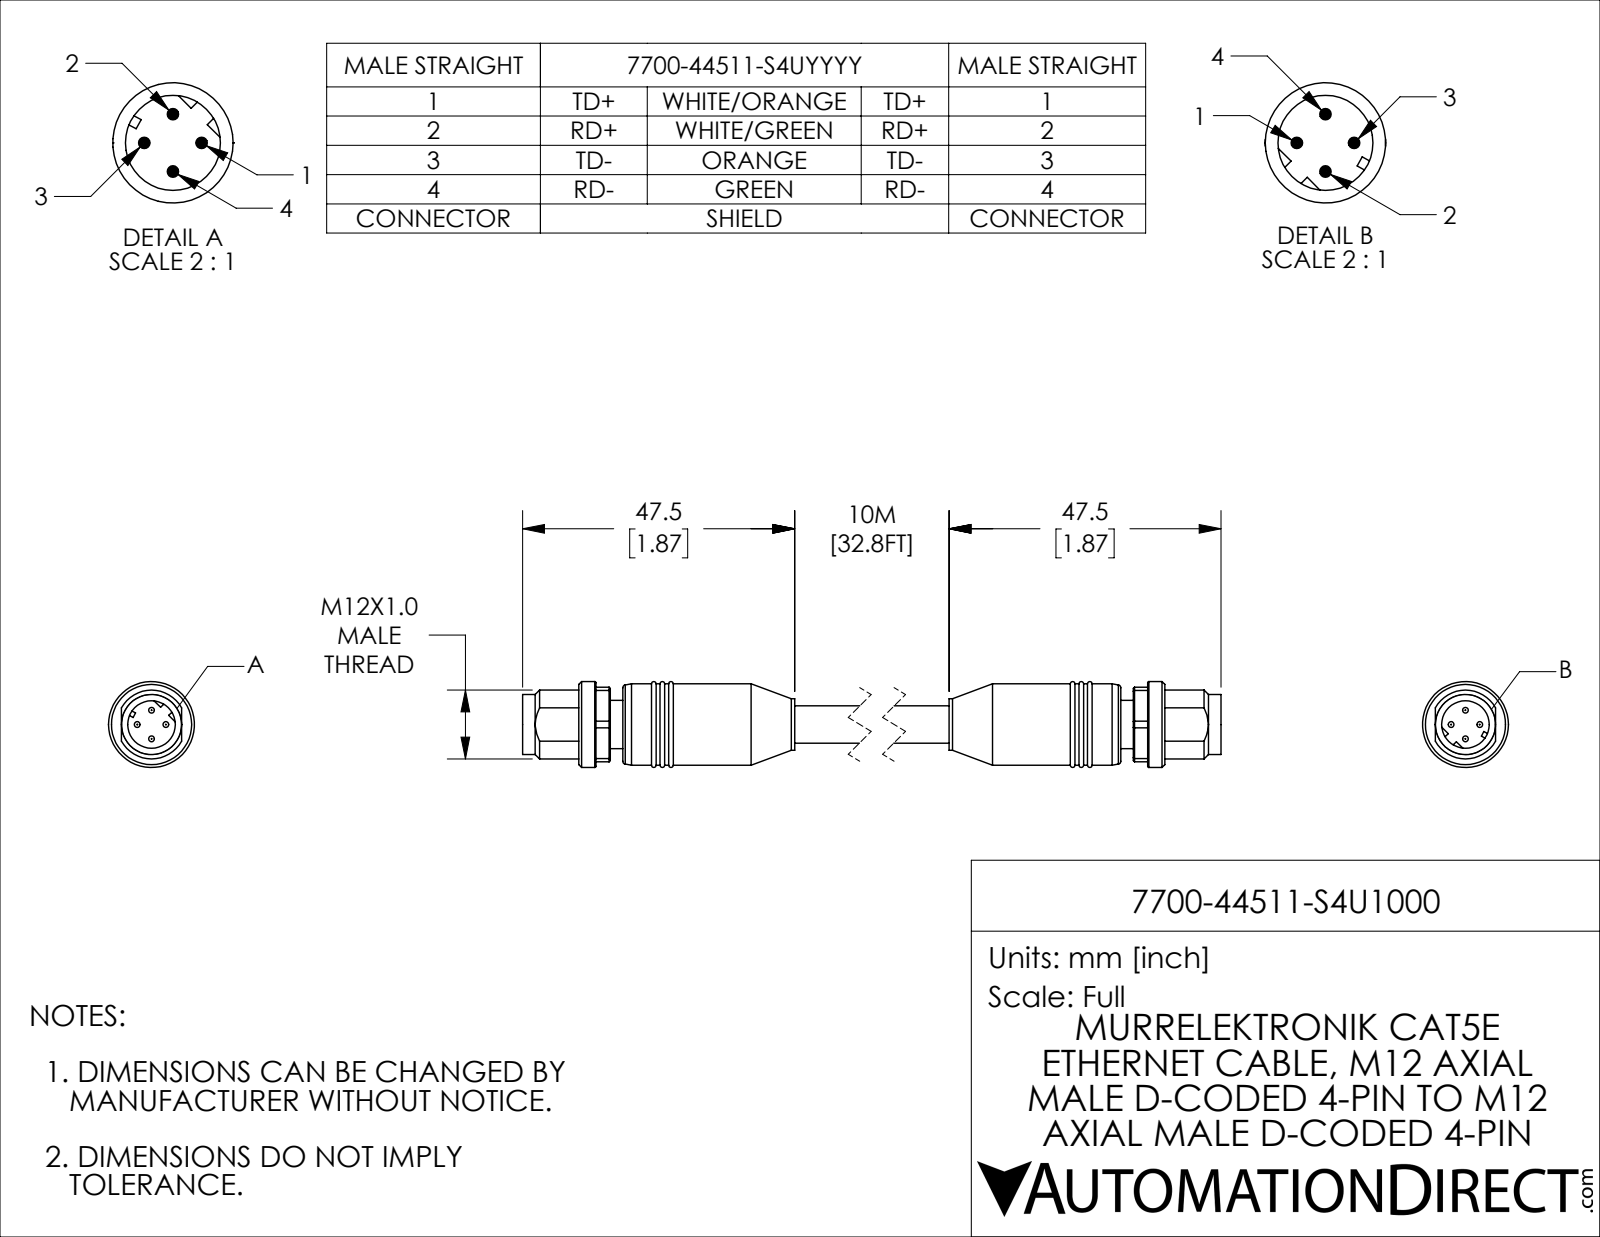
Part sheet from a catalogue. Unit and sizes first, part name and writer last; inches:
Units: inches
Overall size (bounding box): 5.815 × 0.591 × 0.591
Round holes (diameter × count): ⌀0.327 ×1
Round bosses / shafts (diameter × count): ⌀0.039 ×4, ⌀0.591 ×1, ⌀0.559 ×1, ⌀0.413 ×1, ⌀0.354 ×1, ⌀0.331 ×1, ⌀0.256 ×1
Partial cylindrical surfaces — rounded edges, fillets, slot ends (radius × count): R0.236 ×1, R0.283 ×1
Main face-to-face distances: 0.087, 4.524, 0.035, 0.252, 0.339, 4.776, 4.862, 5.079, 0.217, 0.303
Volume: 0.804 in³ · Surface area: 9.846 in²
Bodies: 2 solids, 226 faces (72 planar, 74 cylindrical, 80 other)
Part name (STEP PRODUCT): 7700-44511-S4U1000_1; 7700-44511-S4U1000
STEP written by: SolidWorks 2021 (CONFIG_CONTROL_DESIGN)
